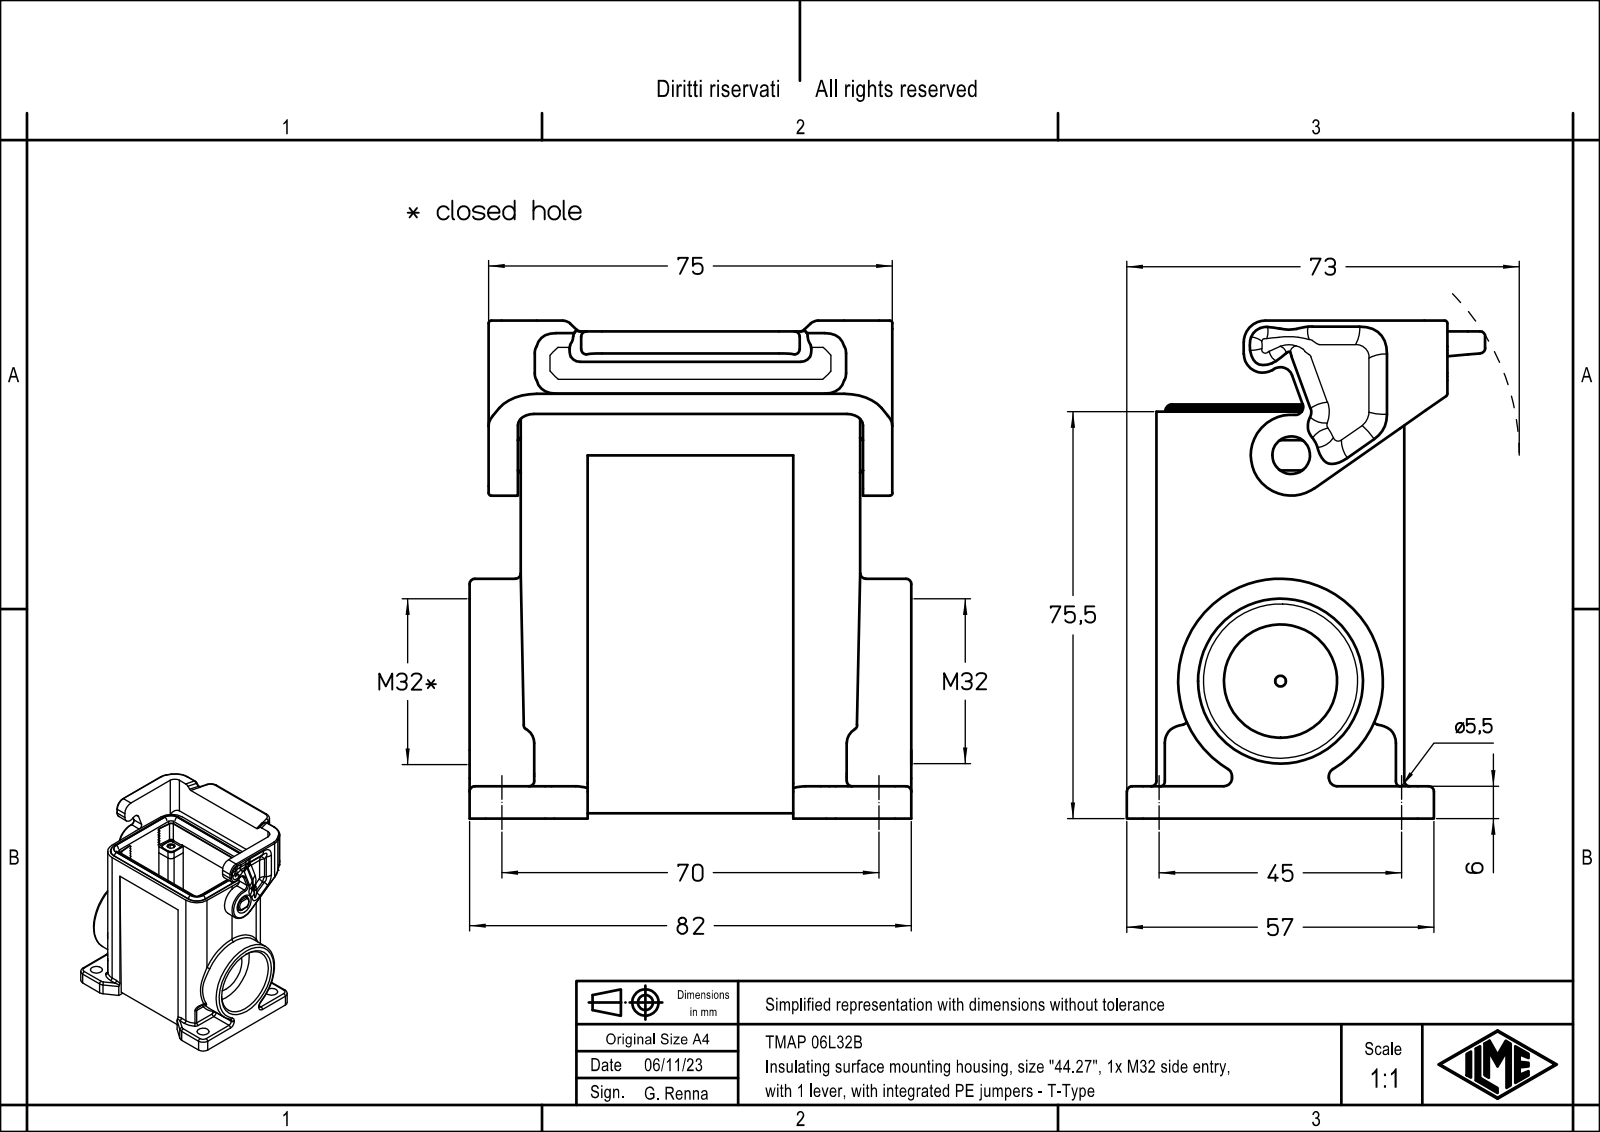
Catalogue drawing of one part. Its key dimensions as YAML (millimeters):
part_name: "TMAP 06L32B"
step_written_by: "Creo Elements/Direct Modeling 20.1B 02-Apr-2019 (C) Parametric Technology GmbH (AUTOMOTIVE_DESIGN)"
units: millimeters
bodies: {solids: 1, faces: 518, planar: 318, cylindrical: 164, other: 36}
overall_size: [92.4, 82, 66.5]
volume: 125945
surface_area: 50523
round_holes:
  - {diameter: 3.5, count: 4}
  - {diameter: 5.5, count: 4}
  - {diameter: 28, count: 1}
  - {diameter: 30.6, count: 1}
round_bosses_or_shafts:
  - {diameter: 38, count: 1}
partial_cylinders:
  - {radius: 1.5, count: 17}
  - {radius: 3, count: 17}
  - {radius: 2, count: 14}
  - {radius: 1.3, count: 12}
  - {radius: 1, count: 8}
  - {radius: 0.5, count: 6}
  - {radius: 1.6, count: 4}
  - {radius: 6, count: 4}
face_to_face_distances: [5.4, 40.6, 46, 35.2, 5.5, 1, 14.9, 6.1, 9, 58.1]
hole_center_spacings: [15.81, 38.28, 57.71, 67.42, 27, 44, 45, 51.62]
